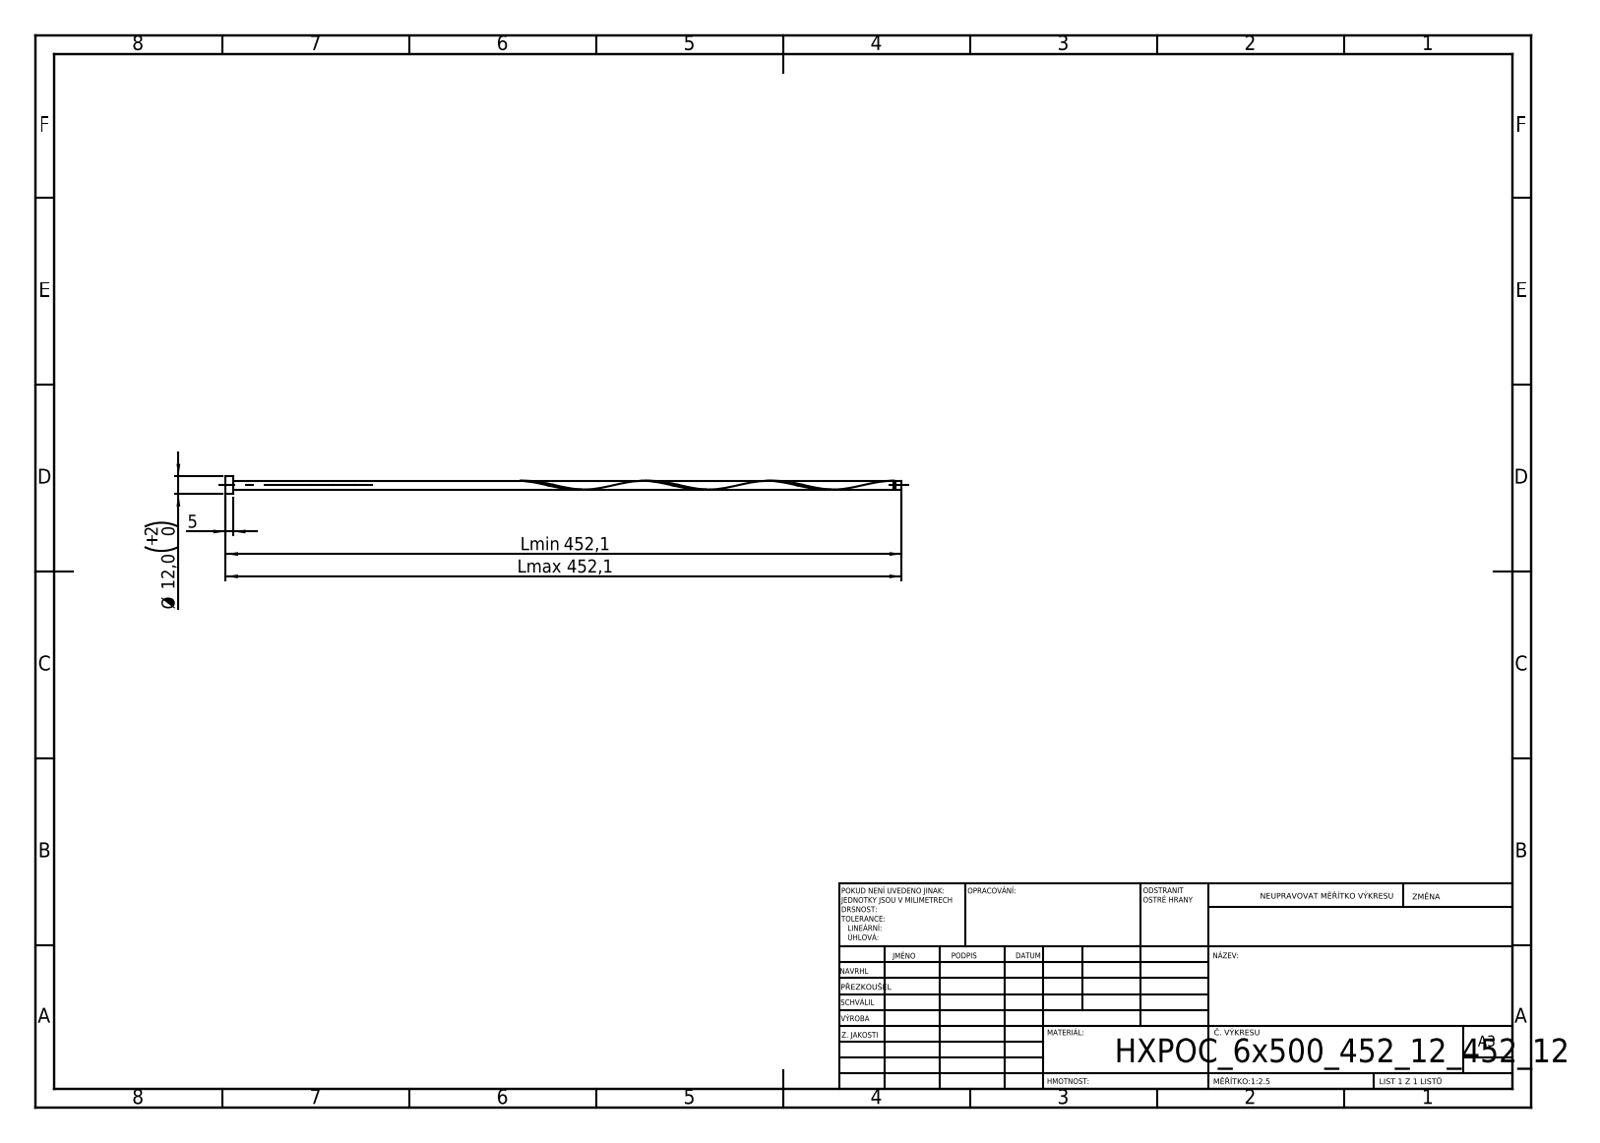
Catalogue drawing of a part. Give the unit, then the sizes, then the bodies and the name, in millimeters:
Units: millimetres
Overall size (bounding box): 452.12 × 12 × 12
Round bosses / shafts (diameter × count): ⌀12 ×1, ⌀6 ×1, ⌀4.8 ×1
Main face-to-face distances: 5, 452.12, 447.12, 448.05, 443.05, 4.07, 446.85, 441.85, 1.2, 5.27
Volume: 16 201 mm³ · Surface area: 12 146 mm²
Bodies: 1 solid, 16 faces (6 planar, 9 cylindrical, 1 other)
STEP written by: SolidWorks 2019 (CONFIG_CONTROL_DESIGN)
